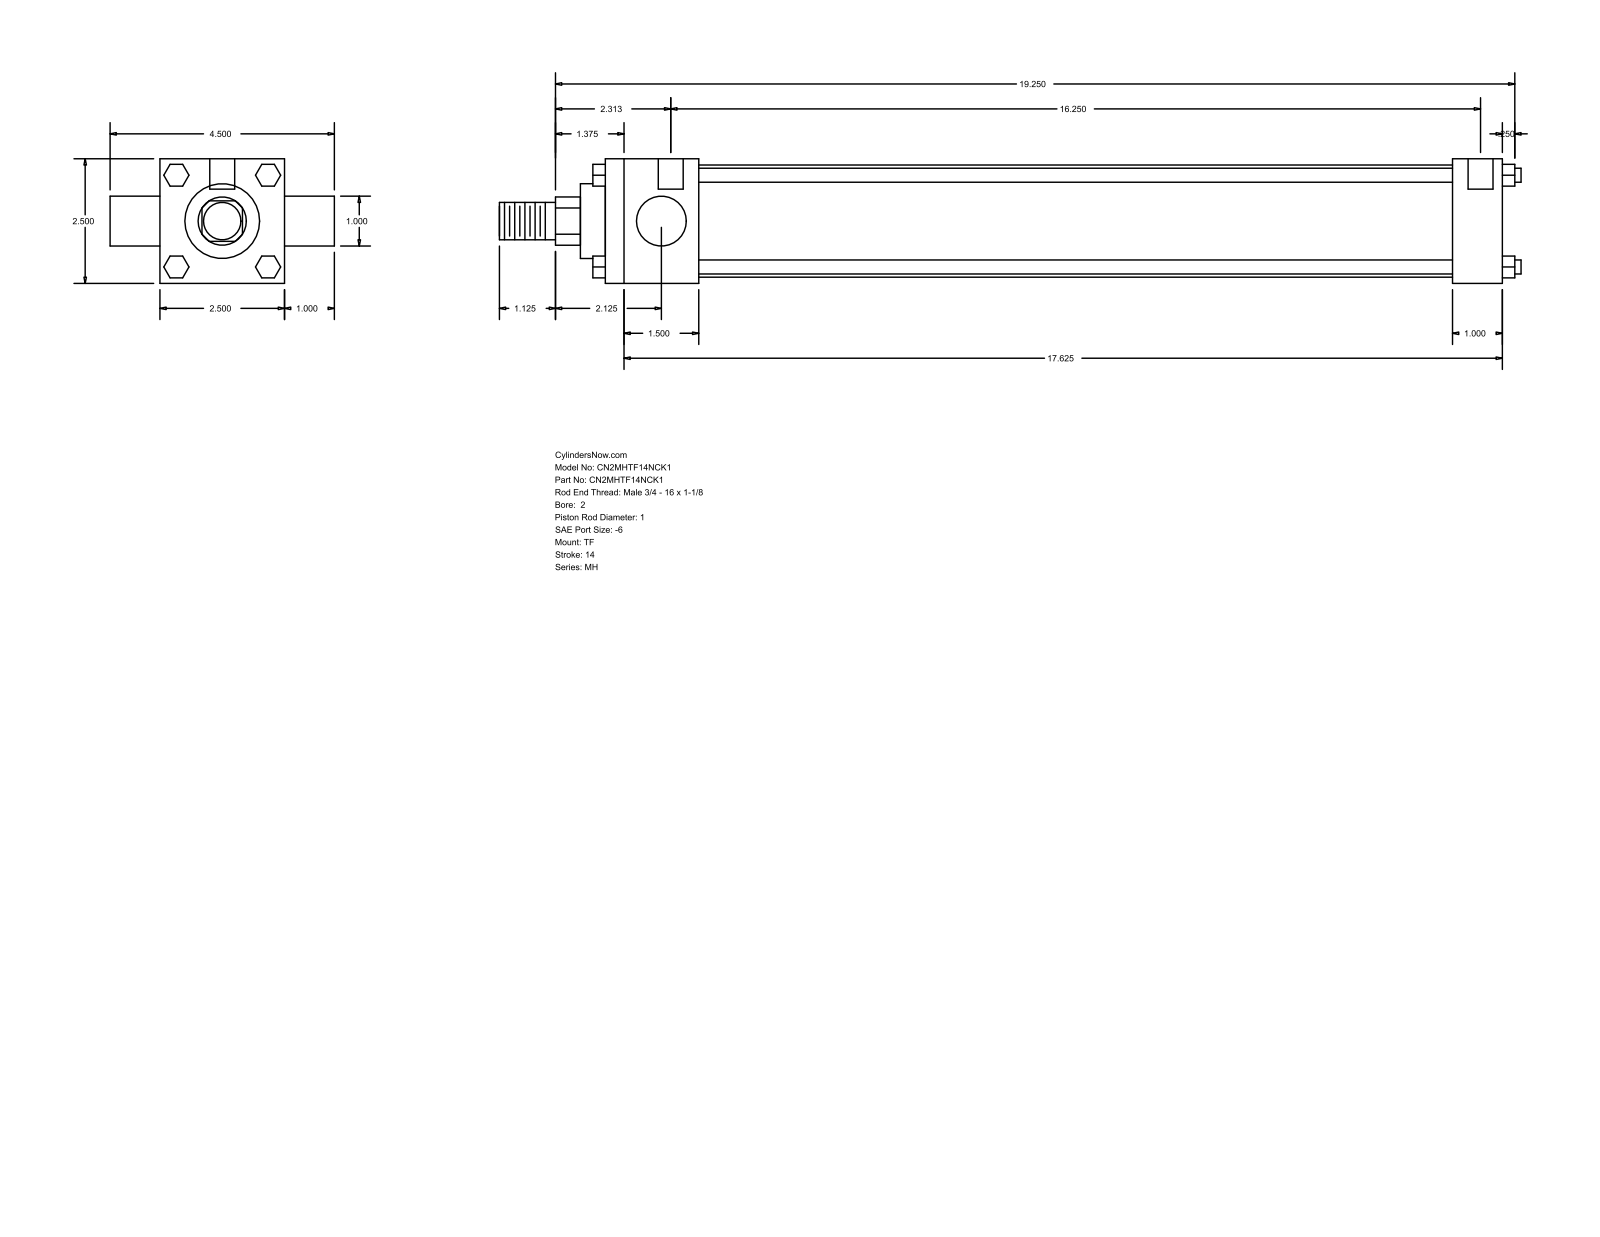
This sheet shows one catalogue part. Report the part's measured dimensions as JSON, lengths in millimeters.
{"part_name": "MH_TF__0200_1", "step_written_by": "GSSL Pune (CONFIG_CONTROL_DESIGN)", "units": "millimeters", "bodies": {"solids": 0, "faces": 120, "planar": 92, "cylindrical": 28, "other": 0}, "overall_size": [520.7, 114.3, 63.5], "round_holes": [[5.56, 3], [12.7, 2]], "round_bosses_or_shafts": [[7.14, 4], [25.4, 2], [57.15, 1], [38.1, 1], [19.05, 1]], "partial_cylinders_radius": [[12.29, 1]], "face_to_face_distances": [63.5, 457.2, 25.4, 47.63, 431.8, 384.17, 409.57, 88.9, 469.9, 6.35], "hole_center_spacings": [3.17, 4.76, 412.75, 415.92, 417.51, 420.68]}
